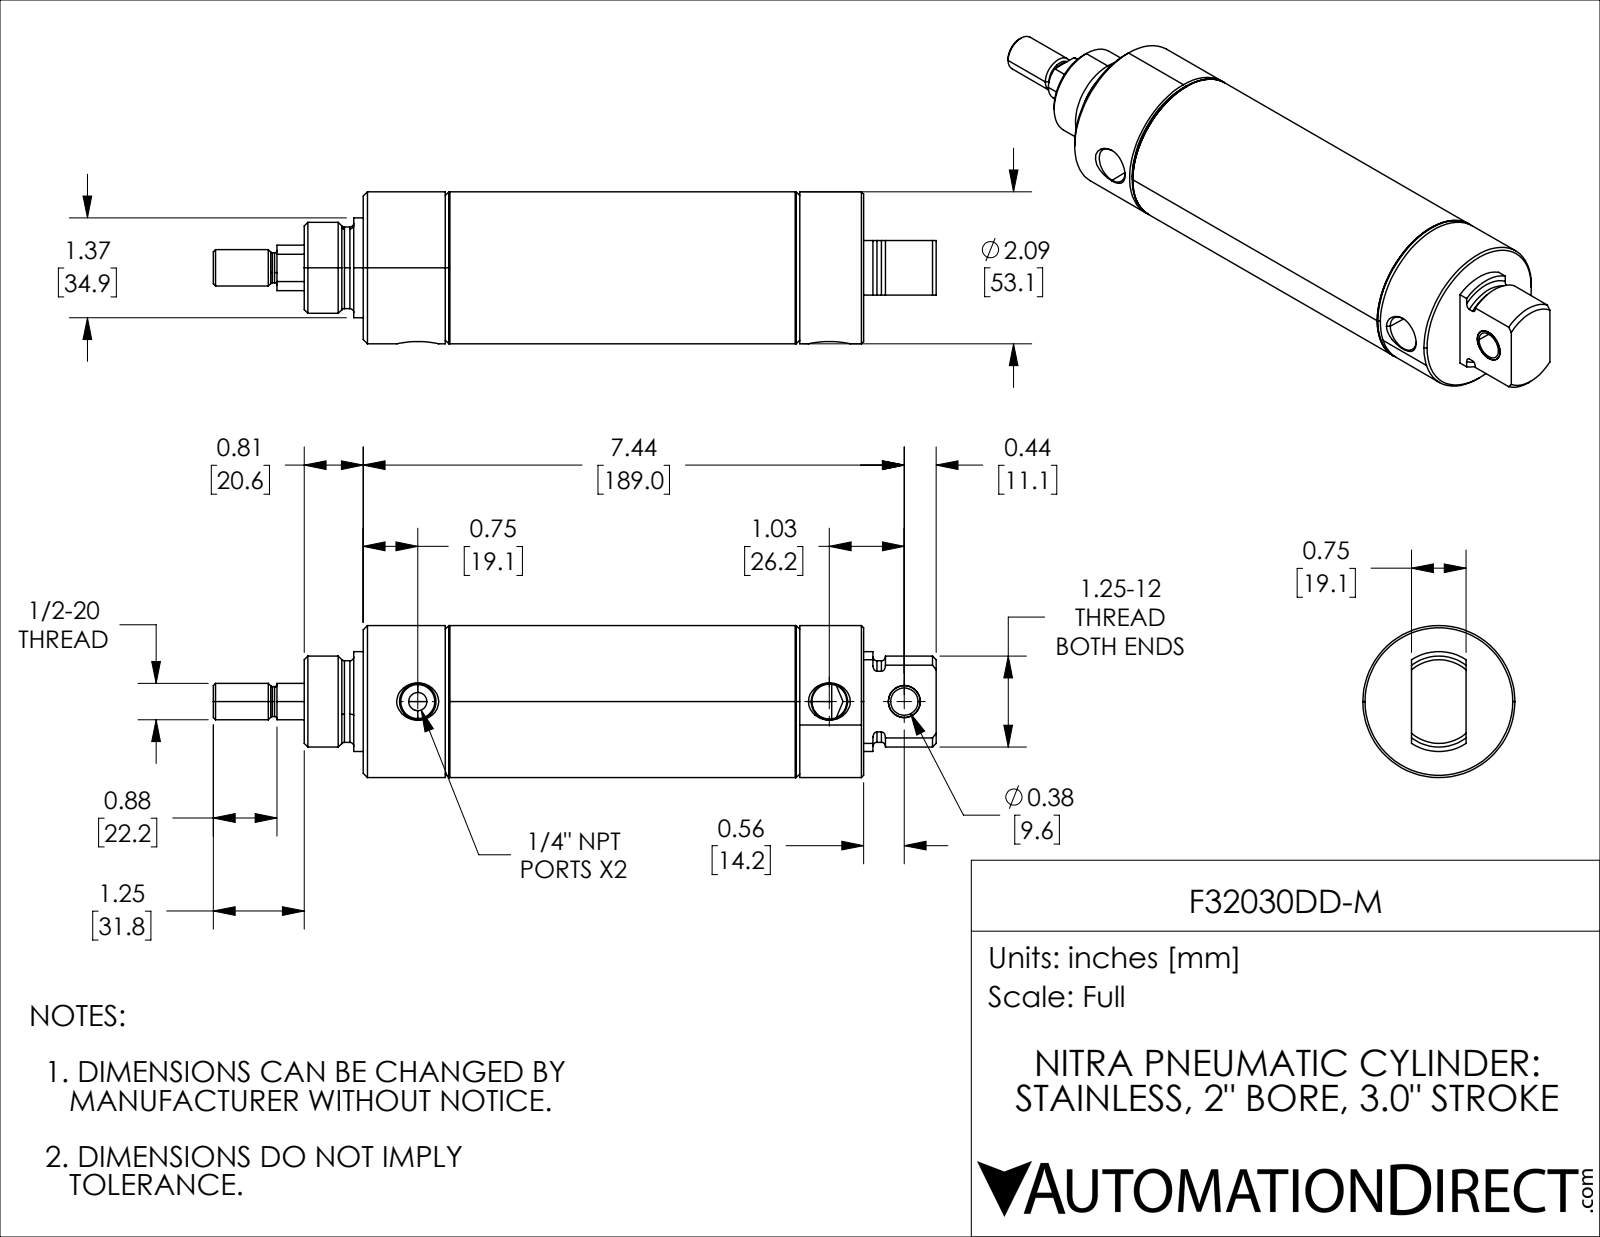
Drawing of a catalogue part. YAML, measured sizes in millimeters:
part_name: "F32030DD-M; F32030DD-M_3; F32030DD-M_5; F32030DD-M_7 (+2 more)"
step_written_by: "SolidWorks 2021 (CONFIG_CONTROL_DESIGN)"
units: millimeters
bodies: {solids: 5, faces: 160, planar: 31, cylindrical: 60, other: 69}
overall_size: [252.43, 53.09, 53.09]
volume: 262887
surface_area: 90807
round_holes:
  - {diameter: 6.35, count: 1}
  - {diameter: 9.55, count: 1}
  - {diameter: 11.15, count: 1}
  - {diameter: 12.18, count: 1}
  - {diameter: 16.52, count: 1}
  - {diameter: 19.05, count: 1}
  - {diameter: 49.05, count: 1}
round_bosses_or_shafts:
  - {diameter: 53.09, count: 1}
  - {diameter: 51.16, count: 1}
  - {diameter: 34.87, count: 1}
  - {diameter: 31.75, count: 1}
  - {diameter: 28.51, count: 1}
  - {diameter: 15.88, count: 1}
  - {diameter: 12.7, count: 1}
  - {diameter: 11.15, count: 1}
partial_cylinders:
  - {radius: 14.25, count: 1}
face_to_face_distances: [30.17, 76.2, 106.37, 136.6, 60.4, 30.23, 106.38, 30.18, 30.22, 38.15]
hole_center_spacings: [26.16, 26.17, 143.76, 169.92, 169.93]
